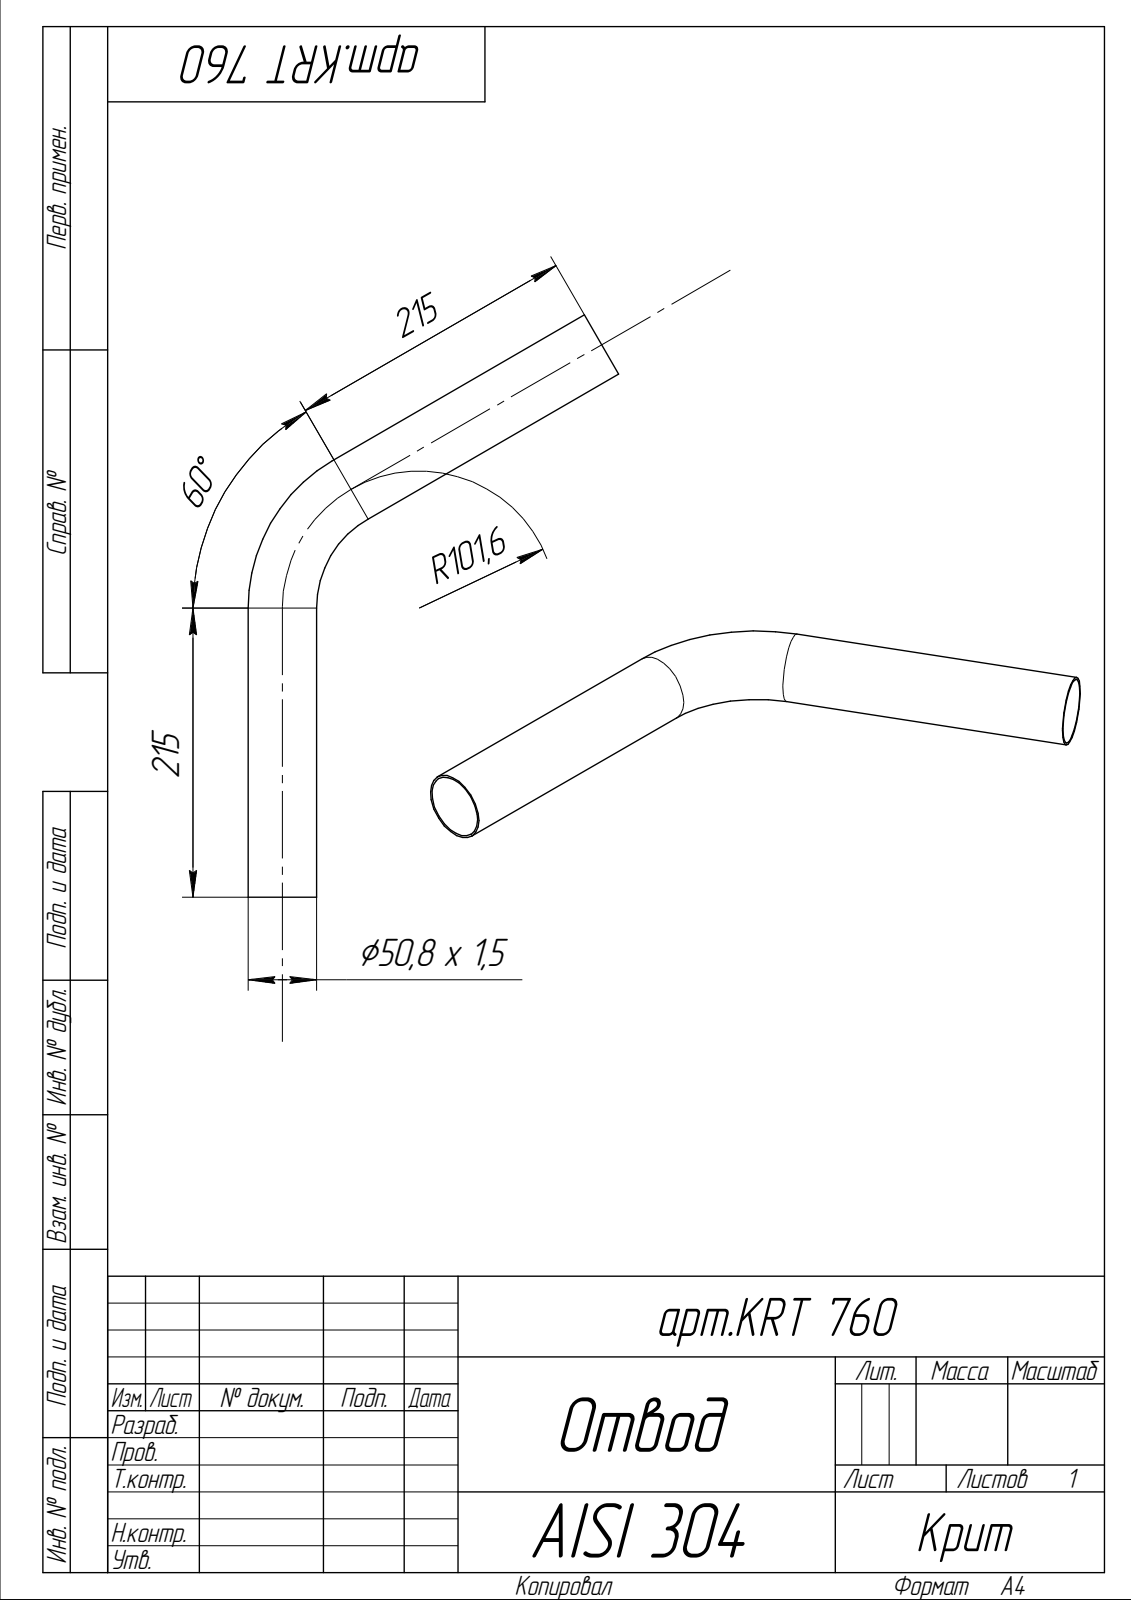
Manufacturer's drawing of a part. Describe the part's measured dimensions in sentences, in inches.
The part is named "Деталь". Its 3-D file was written by "ASCON Math Kernel (AUTOMOTIVE_DESIGN)". It is 1 solid with 8 faces: 2 planar, 4 cylindrical and 2 other. Overall it measures 17.027 by 10.831 by 2 inches. Its volume is 7.605 cubic inches and its surface area 258.3 square inches. Round holes: 2 of diameter 1.882. Round bosses or shafts: 2 of diameter 2.
